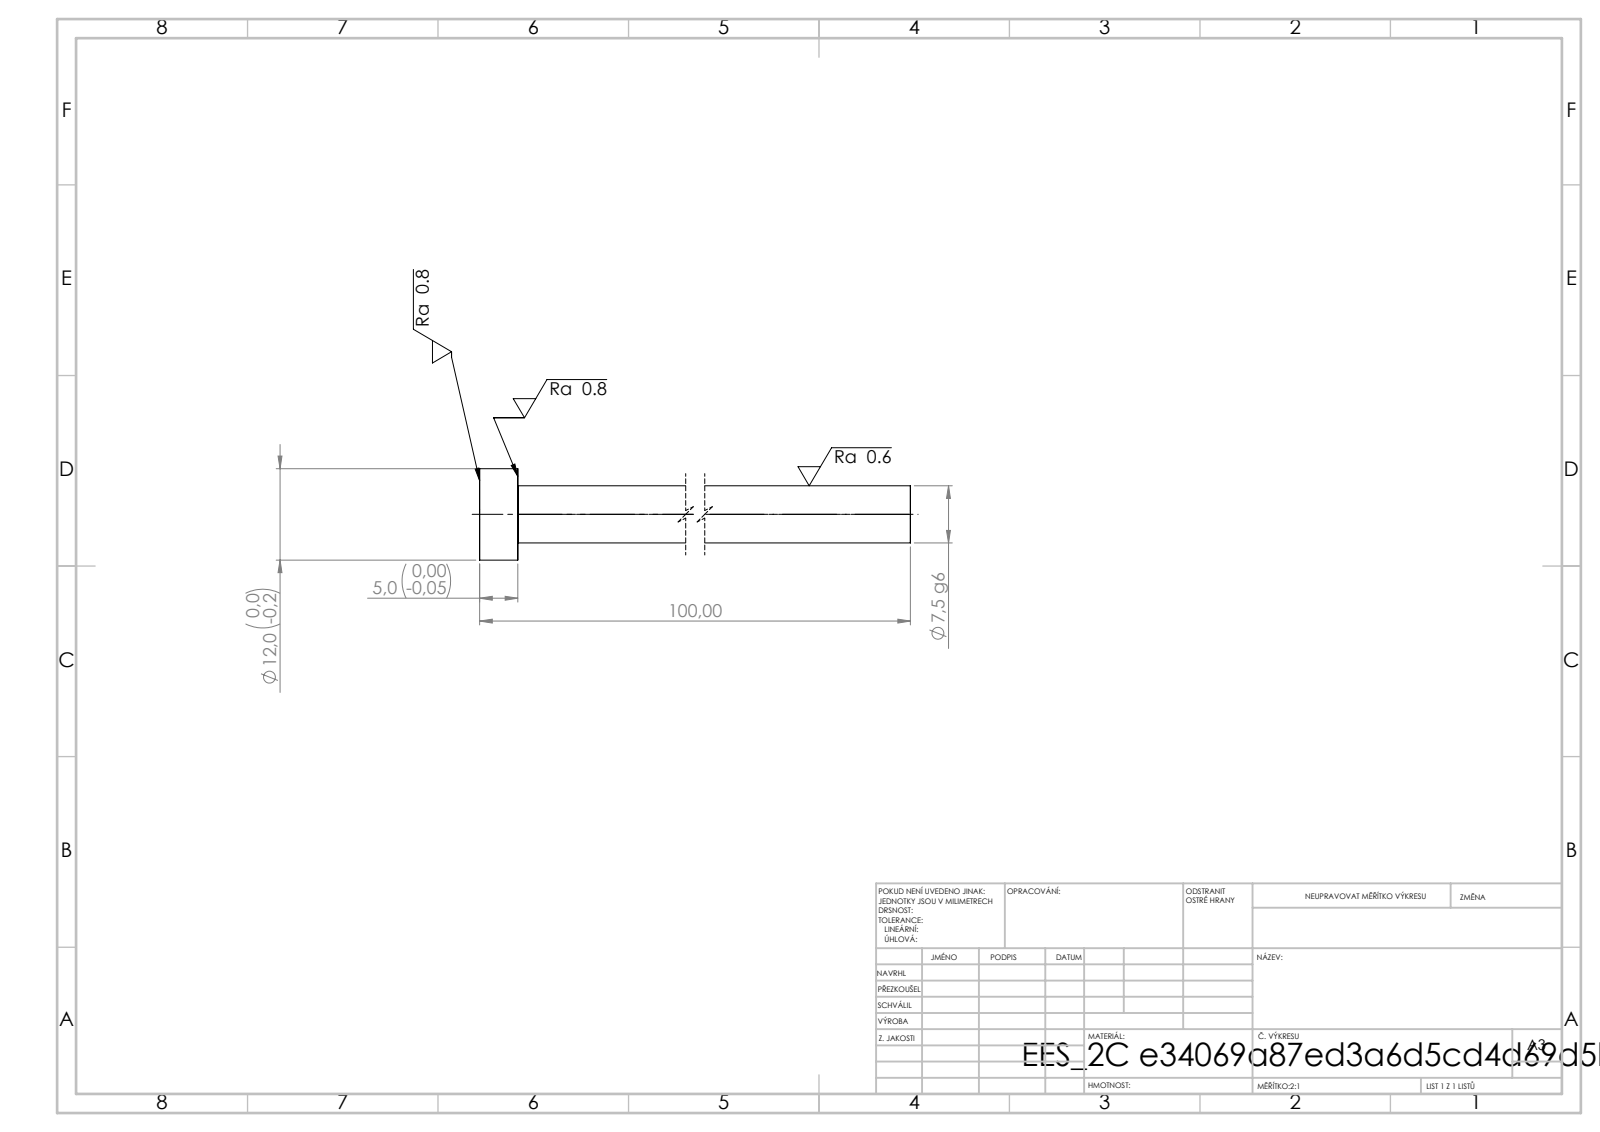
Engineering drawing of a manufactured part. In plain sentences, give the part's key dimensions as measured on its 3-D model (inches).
Its 3-D file was written by "SolidWorks 2019 (CONFIG_CONTROL_DESIGN)". It is 1 solid with 7 faces: 3 planar, 4 cylindrical and 0 other. Overall it measures 3.937 by 0.472 by 0.472 inches. Its volume is 0.291 cubic inches and its surface area 4.112 square inches. Round bosses or shafts: 1 of diameter 0.472, 1 of diameter 0.295. The main face-to-face distances are 0.197, 3.937, 3.74.
